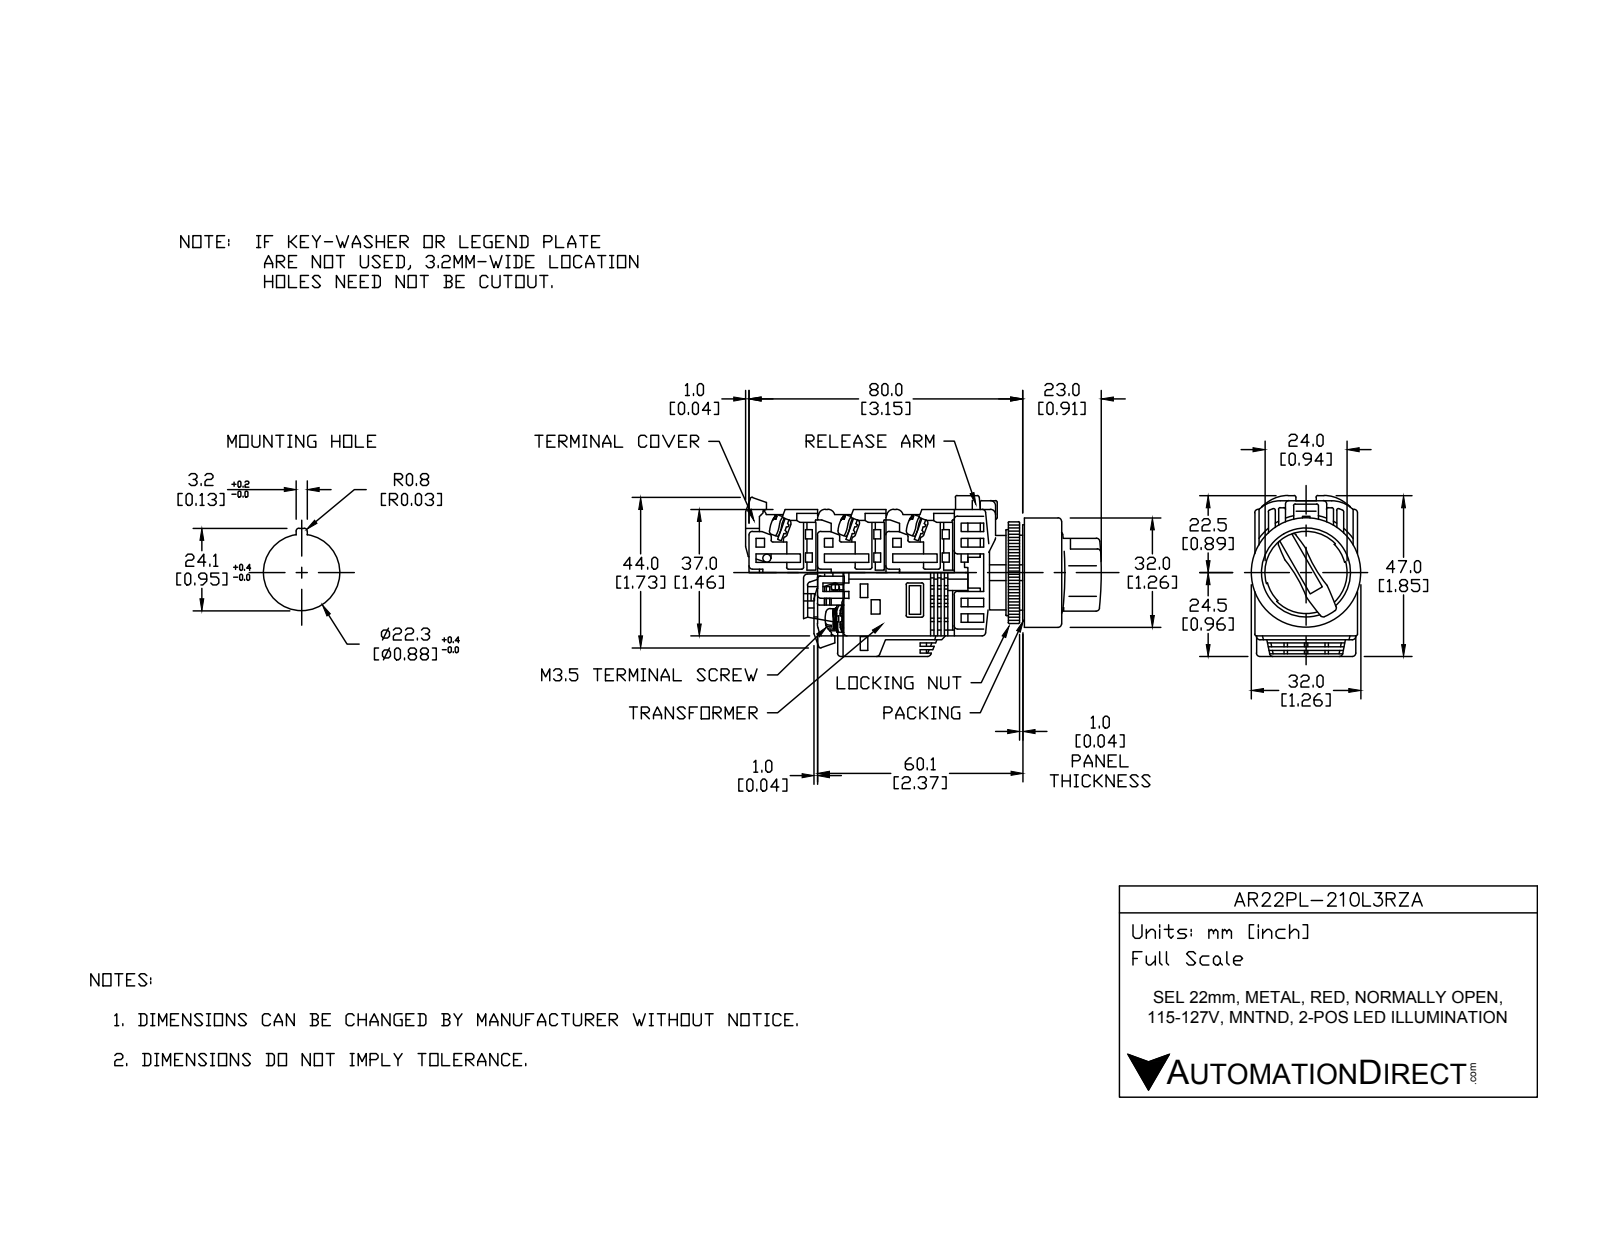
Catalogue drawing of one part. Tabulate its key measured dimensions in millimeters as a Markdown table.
| quantity | value |
| --- | --- |
| part name | AR22PL-210L3RZA |
| STEP written by | SolidWorks 2017 (AUTOMOTIVE_DESIGN) |
| units | millimeters |
| bodies | 18 solids, 462 faces (317 planar, 118 cylindrical, 27 other) |
| overall size | 84.5 × 43.81 × 32 |
| volume | 48 971 mm³ |
| surface area | 26 711 mm² |
| round holes (diameter × count) | 21.8 × 1, 22 × 1, 25 × 1, 31 × 1 |
| round bosses / shafts (diameter × count) | 5 × 4, 32 × 1, 30.5 × 1, 29.8 × 1, 24 × 1, 21.75 × 1, 17 × 1 |
| partial cylindrical surfaces (radius × count) | 0.5 × 39, 1.75 × 8, 1 × 6, 5 × 4, 4 × 2, 12 × 1, 16.59 × 1, 17.59 × 1 |
| main face-to-face distances | 1, 18, 29, 20, 3, 28.5, 0.5, 2, 21, 10 |
